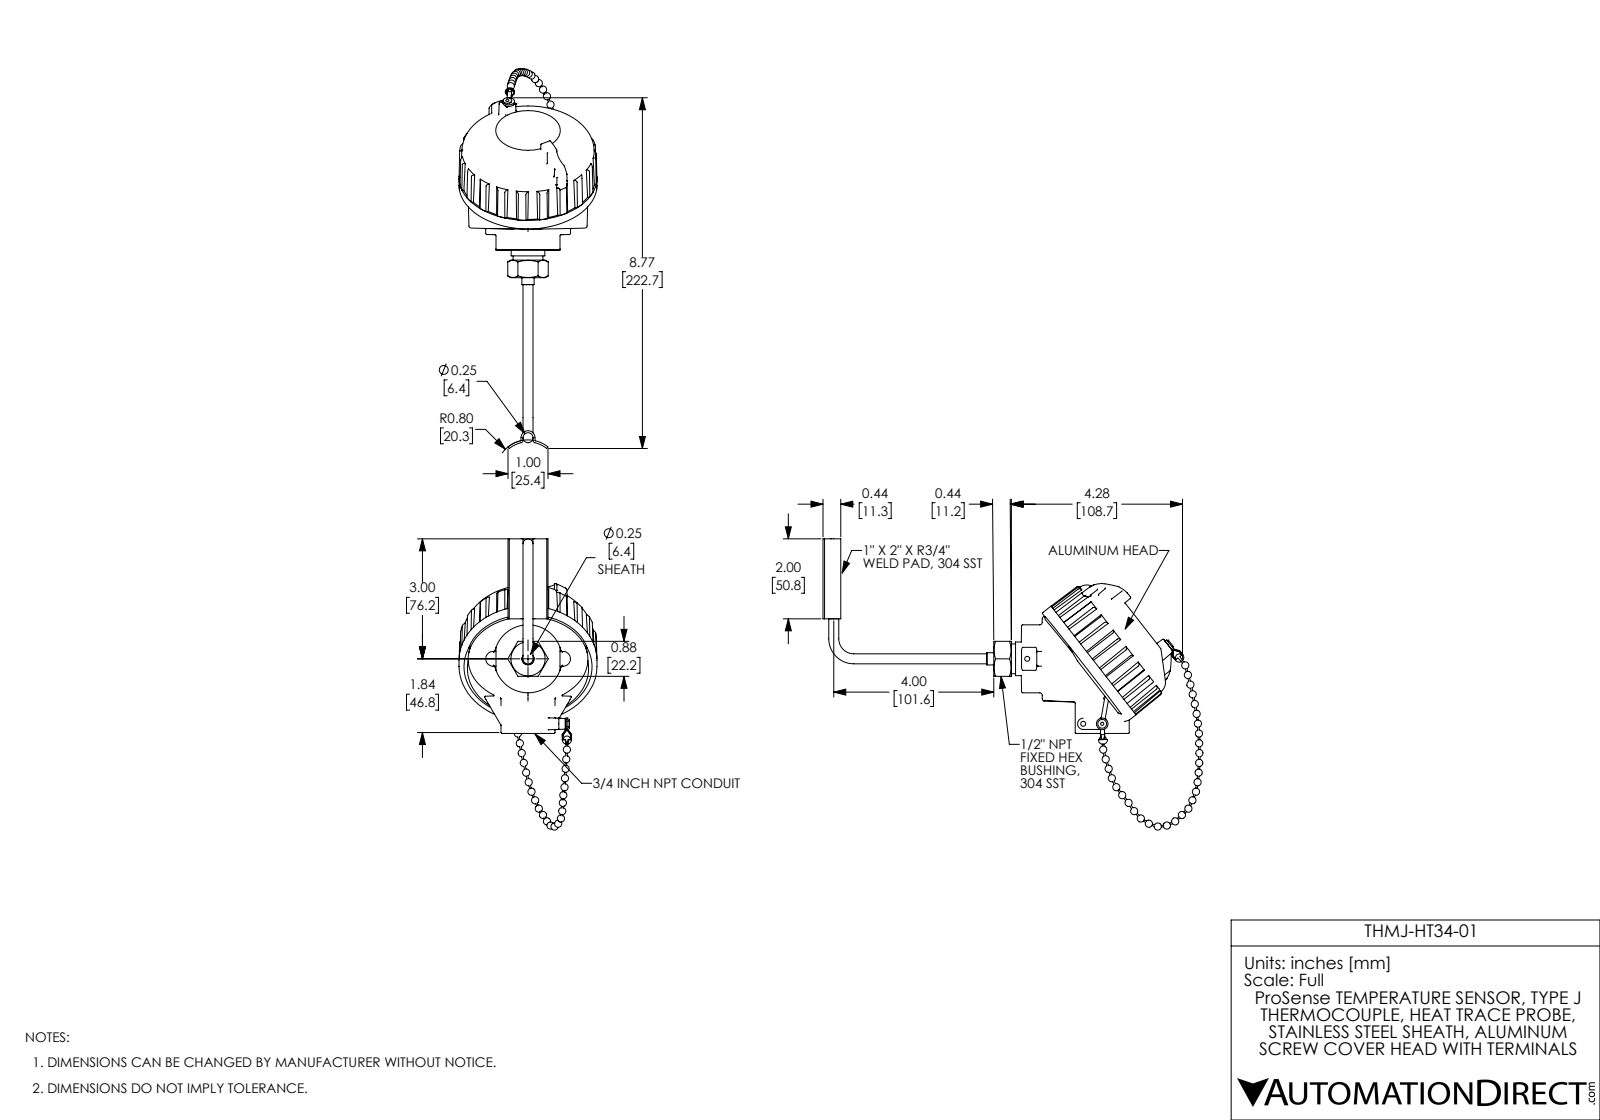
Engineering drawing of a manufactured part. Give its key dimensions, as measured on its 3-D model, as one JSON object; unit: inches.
{"part_name": "THMJ-HT34-01", "step_written_by": "SolidWorks 2017 (AUTOMOTIVE_DESIGN)", "units": "inches", "bodies": {"solids": 73, "faces": 738, "planar": 231, "cylindrical": 149, "other": 358}, "overall_size": [9.499, 7.283, 3.45], "volume_in3": 21.26, "surface_area_in2": 74.14, "round_holes": [[0.08, 2], [0.125, 2], [0.144, 2], [0.165, 1], [0.25, 1], [0.437, 1], [0.688, 1]], "round_bosses_or_shafts": [[0.04, 31], [0.29, 2], [0.123, 2], [3.45, 1], [1.7, 1], [1.35, 1], [0.745, 1], [0.305, 1]], "partial_cylinders_radius": [[0.03, 11], [0.02, 8], [0.015, 6], [0.01, 2], [0.06, 2], [0.185, 2], [0.175, 1], [0.75, 1]], "face_to_face_distances": [1.792, 0.875, 1.336, 0.675, 0.05, 0.925, 0.625, 0.975, 0.3, 0.025], "hole_center_spacings": [0.033, 0.475, 2.145, 2.481]}
